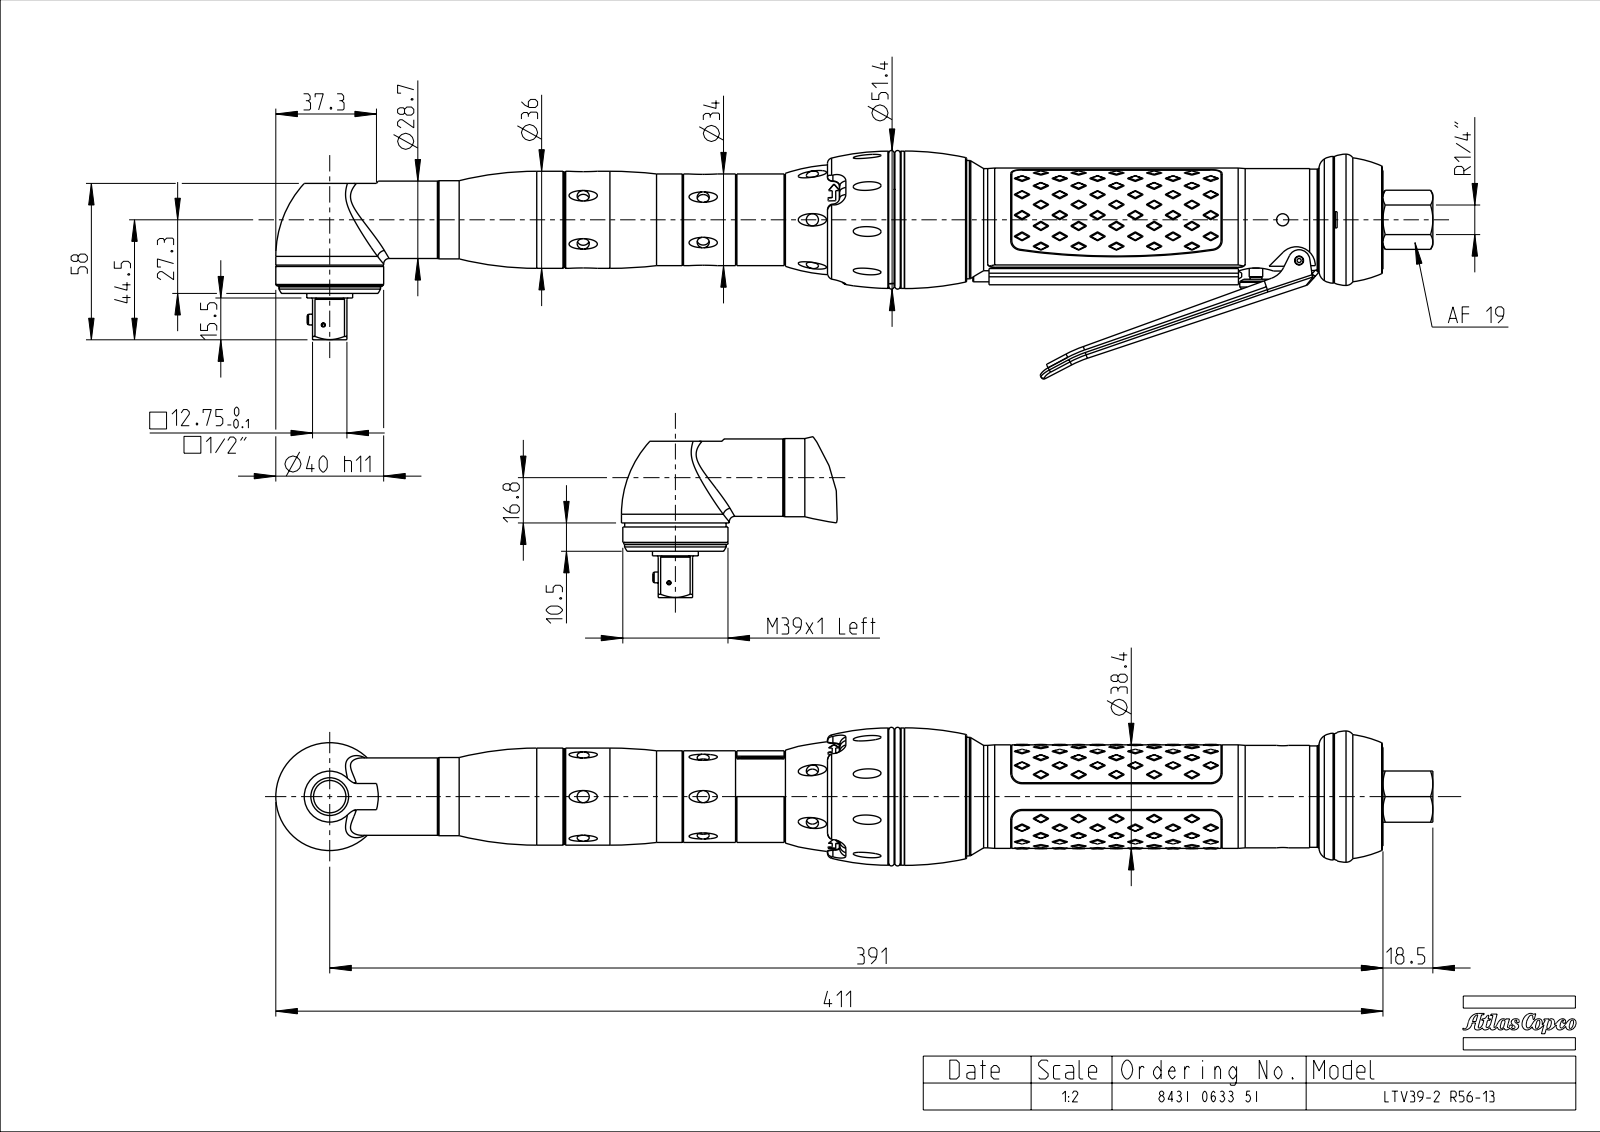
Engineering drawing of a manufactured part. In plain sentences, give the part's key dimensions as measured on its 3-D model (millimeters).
The part is named "TMP152332_SW". Its 3-D file was written by "PRO/ENGINEER BY PARAMETRIC TECHNOLOGY CORPORATION, 2008310 (CONFIG_CONTROL_DESIGN)". It is 0 solids with 1257 faces: 103 planar, 283 cylindrical and 871 other. Overall it measures 429.1 by 84.76 by 51.4 millimeters. Round holes: 14 of diameter 4.5, 10 of diameter 5.5, 1 of diameter 5.2, 1 of diameter 8, 1 of diameter 8.09, 1 of diameter 11, 1 of diameter 11.5, 1 of diameter 11.7, 1 of diameter 13, 1 of diameter 15, 1 of diameter 17.5, 1 of diameter 30. Round bosses or shafts: 2 of diameter 5, 1 of diameter 50.9, 1 of diameter 40.05, 1 of diameter 40, 1 of diameter 39.8, 1 of diameter 38.4, 1 of diameter 38, 1 of diameter 37.7. Partial cylindrical surfaces (rounded edges, fillets, slot ends): 5 of radius 1, 5 of radius 4, 4 of radius 0.7, 3 of radius 0.5, 2 of radius 0.2, 2 of radius 1.5, 2 of radius 2, 2 of radius 2.5. The main face-to-face distances are 19, 3, 1.5, 17.75, 40.8, 155.6, 3.12, 15.88, 152.6, 18. The hole center spacings are 13.5, 25.68, 15.87, 8.34, 21.84, 27, 8.35, 18.38.
